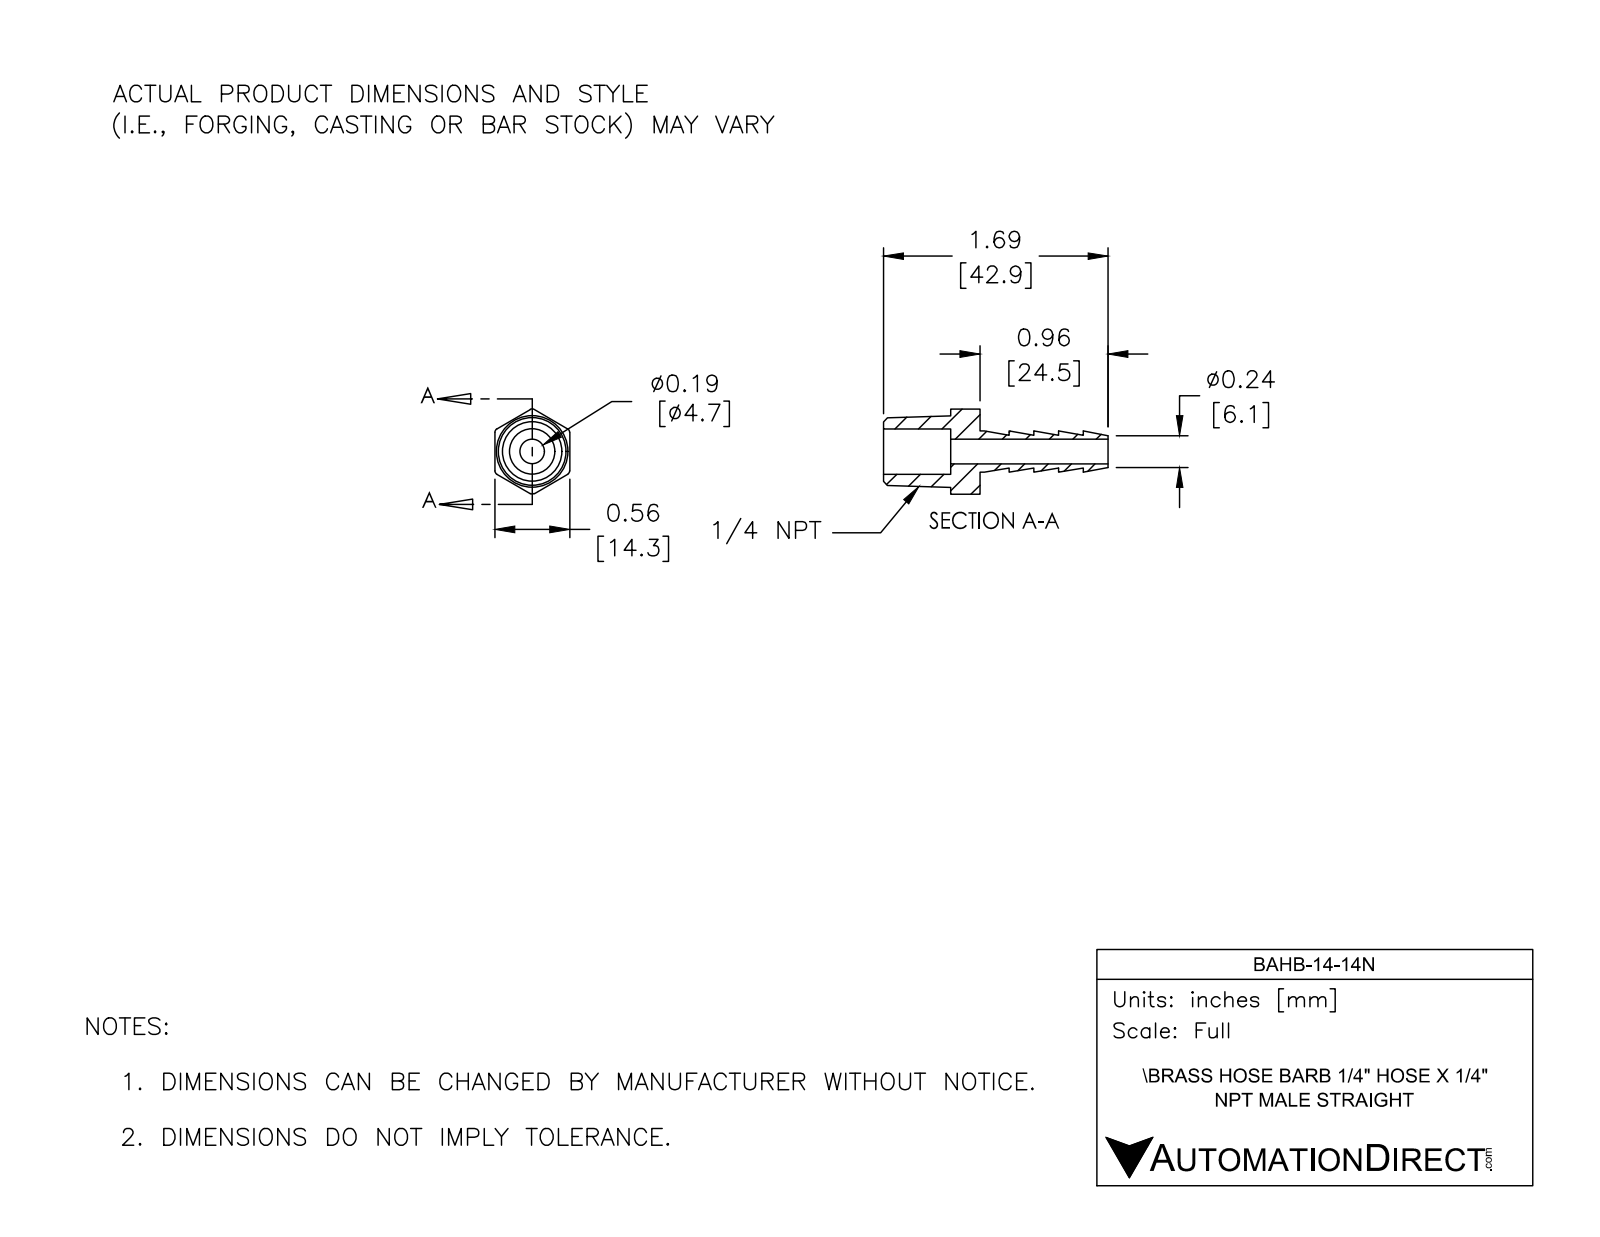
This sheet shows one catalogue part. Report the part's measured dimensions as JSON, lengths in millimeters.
{"part_name": "BAHB-14-14N", "step_written_by": "SolidWorks 2017 (AUTOMOTIVE_DESIGN)", "units": "millimeters", "bodies": {"solids": 1, "faces": 41, "planar": 15, "cylindrical": 12, "other": 14}, "overall_size": [42.9, 16.3, 14.3], "volume_mm3": 2460, "surface_area_mm2": 2496, "round_holes": [[4.7, 1], [8.6, 1]], "round_bosses_or_shafts": [[7.9, 1]], "partial_cylinders_radius": [[0.8, 6]], "face_to_face_distances": [14.3, 5.6, 9.4, 18.4, 12.9, 4.7, 4.7, 14.2, 19.8, 25.3]}
